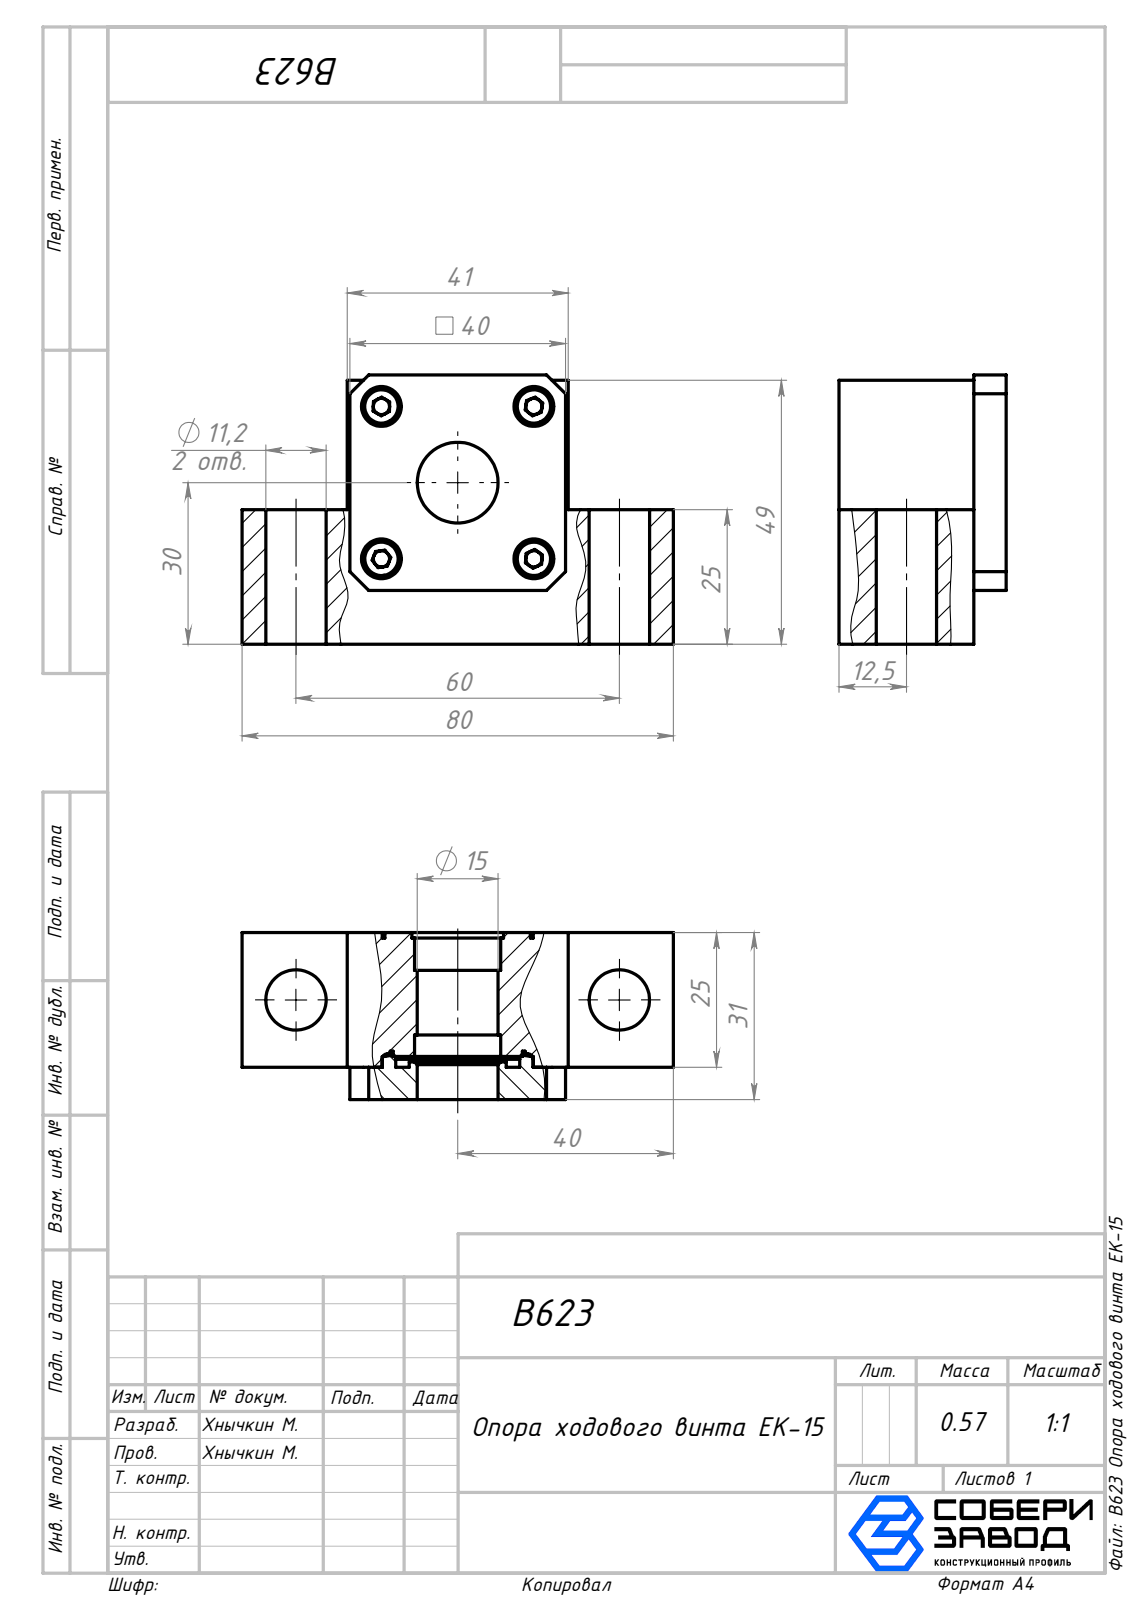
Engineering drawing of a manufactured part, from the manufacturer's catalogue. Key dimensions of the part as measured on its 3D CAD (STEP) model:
Part name (STEP PRODUCT): B623 Опора ходового винта EK-15 корпус_00; socket head cap screw_din_DIN 912 M4 x 6 --- 6N; B623 Крышка_00; B623 Опора ходового винта EK-15
STEP written by: SolidWorks 2026 (AUTOMOTIVE_DESIGN)
Units: millimetres
Bodies: 6 solids, 209 faces (99 planar, 70 cylindrical, 40 other)
Overall size (bounding box): 80 × 50 × 31
Volume: 72 781 mm³ · Surface area: 21 056 mm²
Round holes (diameter × count): ⌀3 ×4, ⌀4.5 ×4, ⌀7.4 ×4, ⌀11.2 ×2, ⌀15 ×1, ⌀16 ×1, ⌀17 ×1, ⌀23 ×1, ⌀25 ×1, ⌀28 ×1
Round bosses / shafts (diameter × count): ⌀7 ×4, ⌀4 ×4, ⌀27 ×1, ⌀24 ×1, ⌀18 ×1
Main face-to-face distances: 25, 6, 31, 19.5, 60.5, 49, 24, 80, 2, 41
Hole centre spacings: 20, 28.28, 39.99, 60
